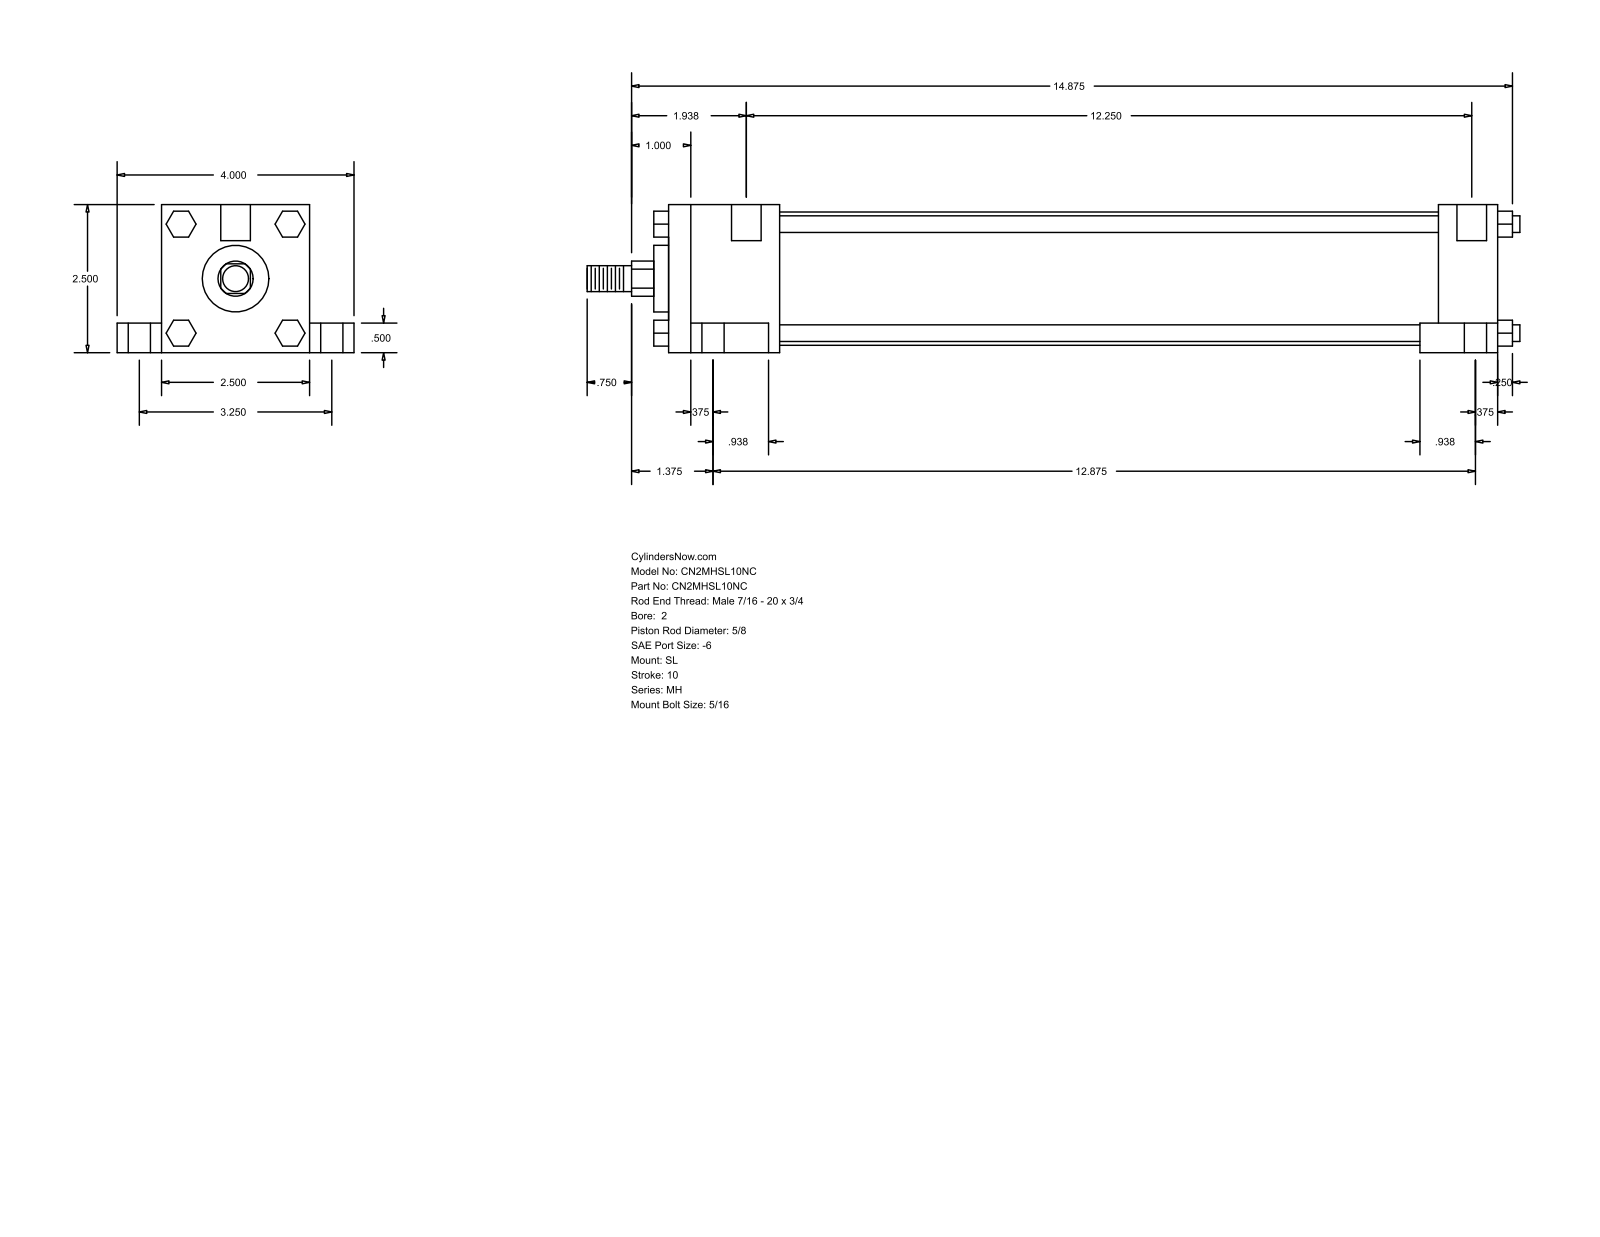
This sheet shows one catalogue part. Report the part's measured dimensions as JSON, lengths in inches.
{"part_name": "MH_SL__0200_0.625", "step_written_by": "GSSL Pune (CONFIG_CONTROL_DESIGN)", "units": "inches", "bodies": {"solids": 0, "faces": 148, "planar": 112, "cylindrical": 36, "other": 0}, "overall_size": [15.75, 4, 2.5], "round_holes": [[0.219, 4], [0.375, 4], [0.625, 4], [0.5, 2]], "round_bosses_or_shafts": [[0.281, 4], [2.25, 1], [1.125, 1], [0.625, 1], [0.437, 1]], "partial_cylinders_radius": [[0.297, 1]], "face_to_face_distances": [2.5, 14, 0.5, 0.75, 3.25, 2, 13, 1, 1.875, 11.125], "hole_center_spacings": [1.626, 1.668, 1.719, 3.25, 12.419, 12.563, 12.605, 12.875]}
